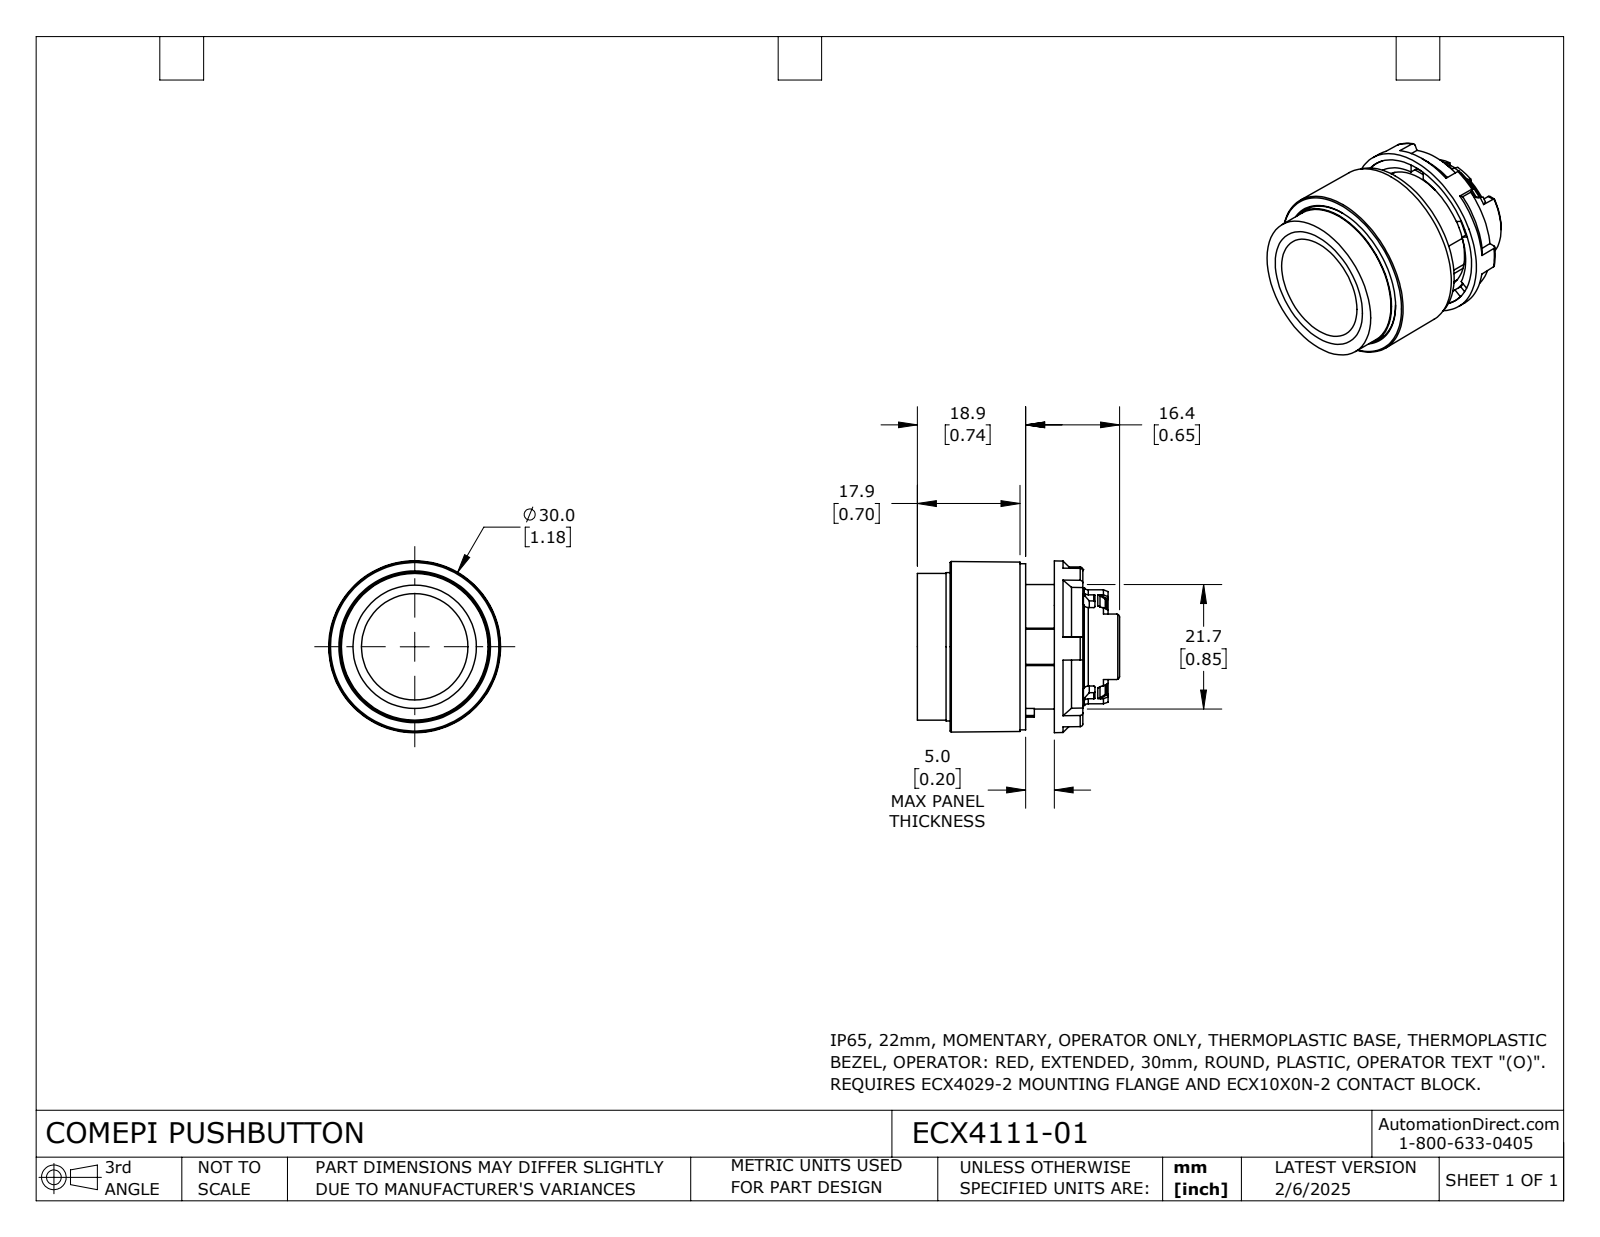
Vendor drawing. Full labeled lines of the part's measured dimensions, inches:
Part name (STEP PRODUCT): ECX4111-01
STEP written by: SolidWorks 2024 (CONFIG_CONTROL_DESIGN)
Units: inches
Bodies: 3 solids, 401 faces (135 planar, 113 cylindrical, 153 other)
Overall size (bounding box): 1.39 × 1.181 × 1.181
Volume: 0.657 in³ · Surface area: 17.27 in²
Round holes (diameter × count): ⌀0.531 ×1, ⌀0.713 ×1, ⌀0.872 ×1
Round bosses / shafts (diameter × count): ⌀1.142 ×1, ⌀1.02 ×1, ⌀1.008 ×1, ⌀0.965 ×1, ⌀0.854 ×1, ⌀0.807 ×1, ⌀0.787 ×1, ⌀0.748 ×1
Partial cylindrical surfaces — rounded edges, fillets, slot ends (radius × count): R0.008 ×24, R0.02 ×8, R0.01 ×2, R0.293 ×1, R0.344 ×1, R0.348 ×1, R0.366 ×1
Main face-to-face distances: 0.409, 0.039, 0.433, 0.236, 0.197, 0.449, 0.217, 0.232, 0.61, 0.177
